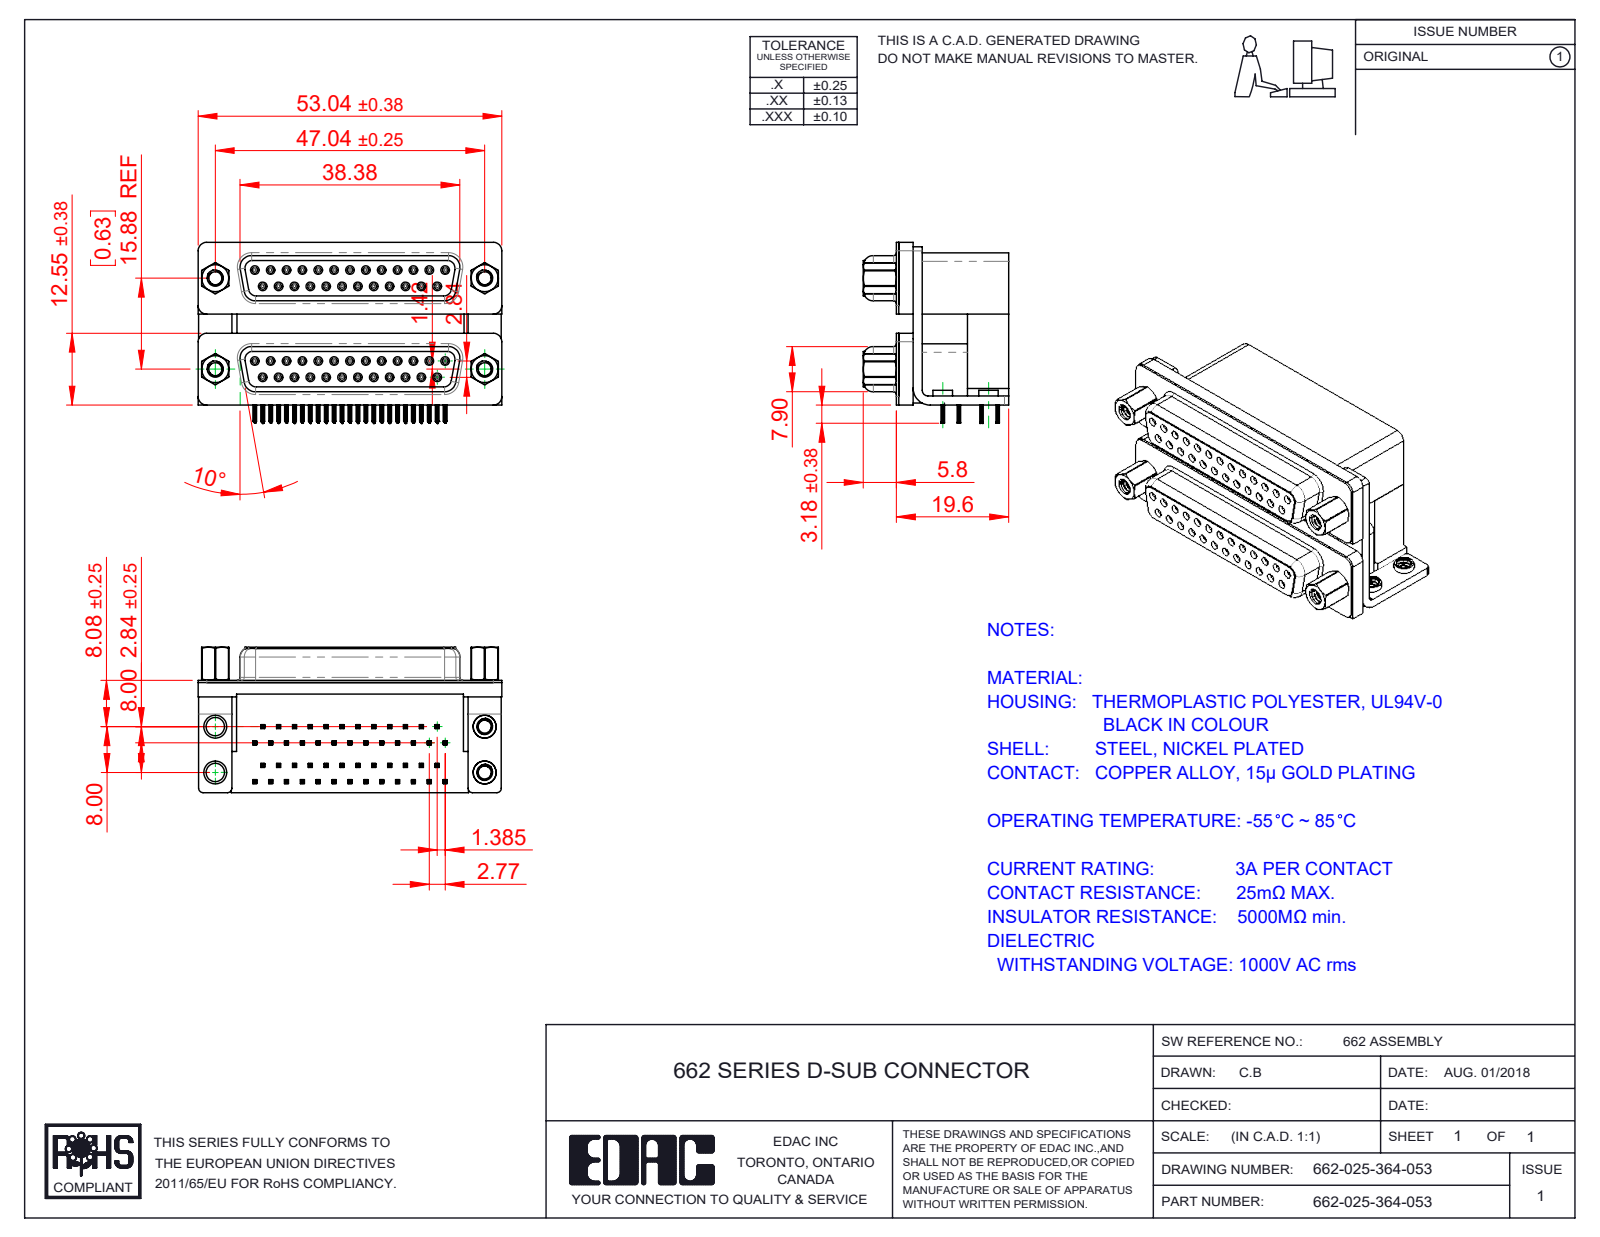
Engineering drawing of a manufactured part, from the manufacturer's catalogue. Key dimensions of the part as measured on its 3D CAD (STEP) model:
Part name (STEP PRODUCT): 662 Housing Upper_25 Contacts L; 662 Housing Spacer_25 Contacts L; 662 Threaded Rivet_4-40; 662 Housing Lower_25 Contacts (+8 more)
STEP written by: SolidWorks 2020 (CONFIG_CONTROL_DESIGN)
Units: millimetres
Bodies: 69 solids, 8184 faces (3632 planar, 2024 cylindrical, 2528 other)
Overall size (bounding box): 53.04 × 31.61 × 25.4
Volume: 23 358 mm³ · Surface area: 26 205 mm²
Round holes (diameter × count): ⌀0.8 ×50, ⌀0.9 ×50, ⌀2.26 ×8, ⌀2.29 ×4, ⌀2.75 ×4, ⌀3.2 ×4, ⌀3.5 ×4, ⌀4 ×4, ⌀4.8 ×4, ⌀5 ×4
Round bosses / shafts (diameter × count): ⌀1.2 ×50, ⌀4.9 ×4, ⌀4.75 ×4, ⌀4 ×4, ⌀3.9 ×4, ⌀3.4 ×4, ⌀2.79 ×4
Partial cylindrical surfaces — rounded edges, fillets, slot ends (radius × count): R0.1 ×400, R0.15 ×200, R0.35 ×100, R0.34 ×50, R0.28 ×24, R1.35 ×18, R1.5 ×13, R0.5 ×8
Main face-to-face distances: 15.88, 0.4, 19.2, 7.2, 12, 10.7, 6.2, 2.9, 16.7, 9.5
Hole centre spacings: 3.16, 2.77, 5.54, 11.08, 8.31, 5.03, 13.85, 7.48
